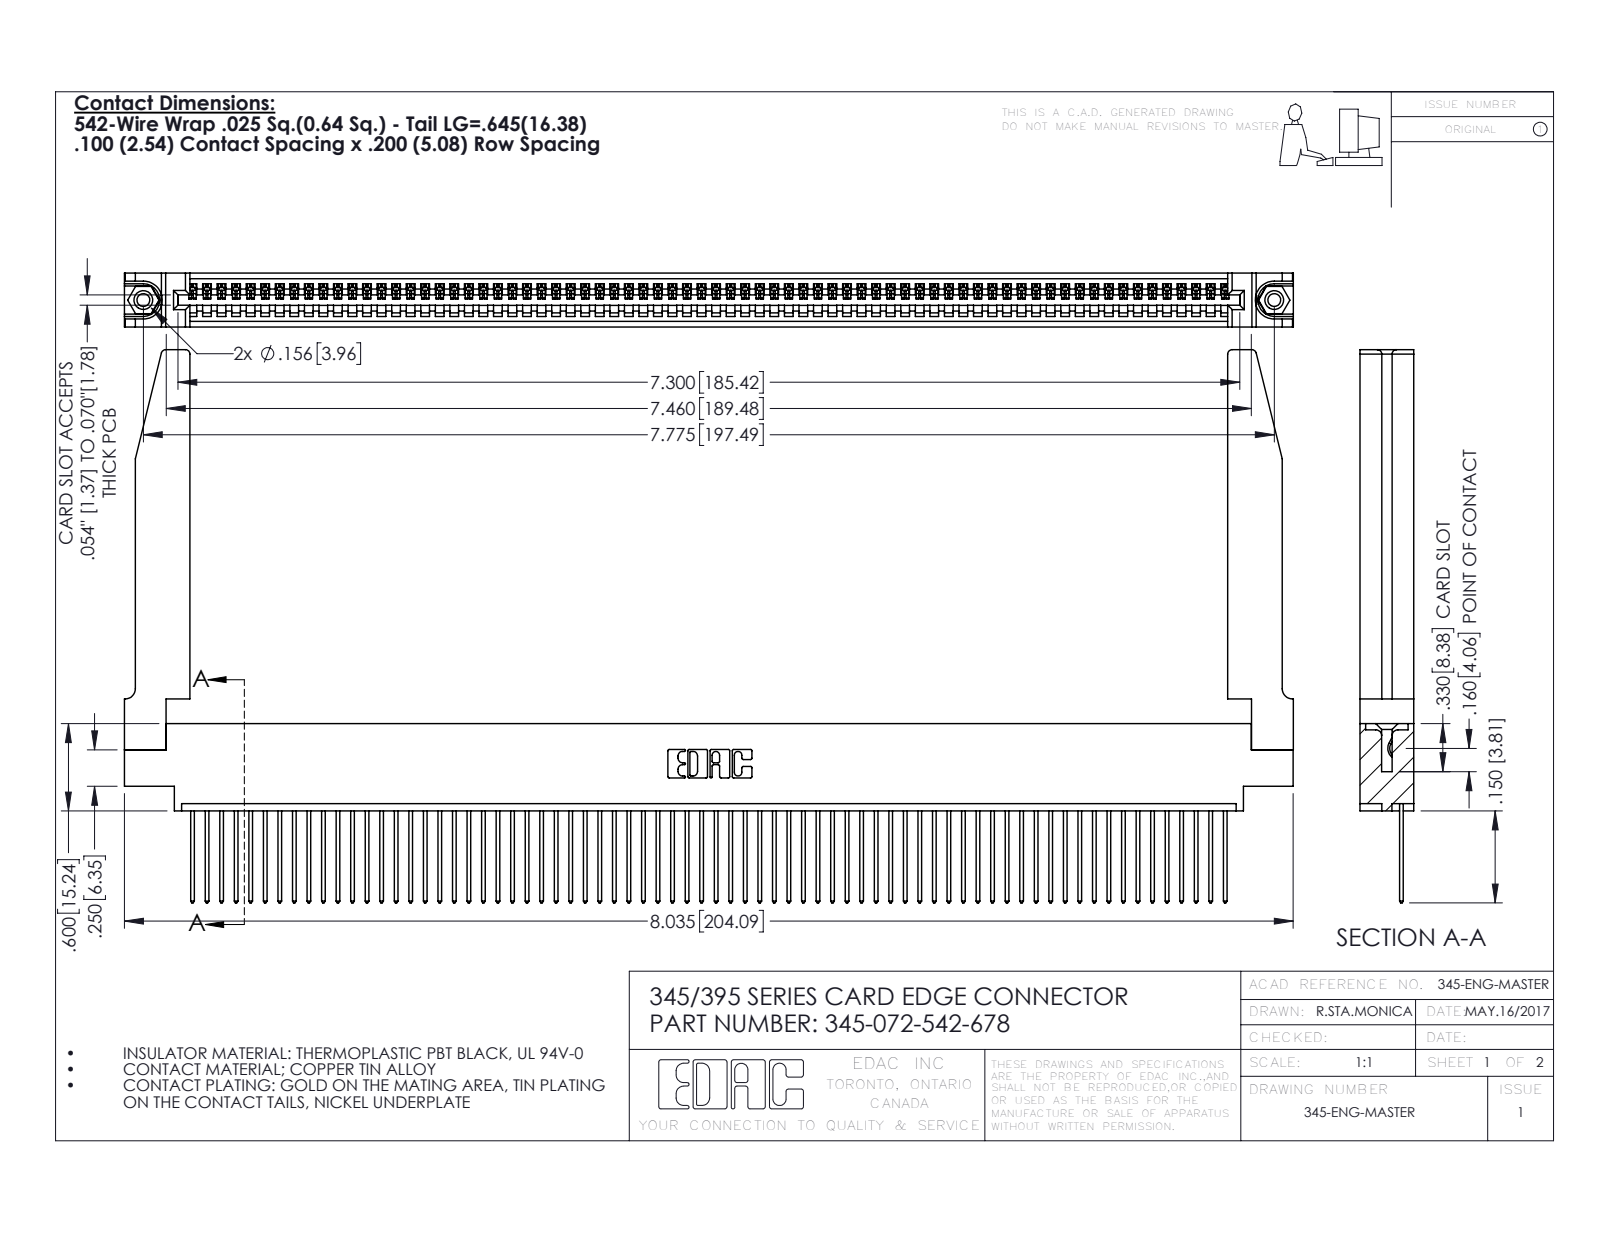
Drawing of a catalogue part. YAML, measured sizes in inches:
part_name: "345-292-001_345-293-142; 345-072-542-678; 345-250-001_345-250-001-102; 345-220-078_345-220-078 (+1 more)"
step_written_by: "SolidWorks 2016 (CONFIG_CONTROL_DESIGN)"
units: inches
bodies: {solids: 77, faces: 4540, planar: 3106, cylindrical: 1382, other: 52}
overall_size: [8.036, 3.802, 0.37]
volume: 1.675
surface_area: 53.55
round_holes:
  - {diameter: 0.089, count: 2}
  - {diameter: 0.125, count: 2}
  - {diameter: 0.156, count: 2}
  - {diameter: 0.064, count: 1}
round_bosses_or_shafts:
  - {diameter: 0.155, count: 2}
partial_cylinders:
  - {radius: 0.006, count: 144}
  - {radius: 0.01, count: 144}
  - {radius: 0.01, count: 22}
  - {radius: 0.03, count: 8}
  - {radius: 0.007, count: 6}
  - {radius: 0.031, count: 6}
  - {radius: 0.026, count: 3}
  - {radius: 0.031, count: 2}
face_to_face_distances: [0.072, 0.298, 0.37, 0.098, 0.272, 0.025, 0.2, 0.225, 0.149, 0.175]
hole_center_spacings: [0.27, 7.539, 7.775]
